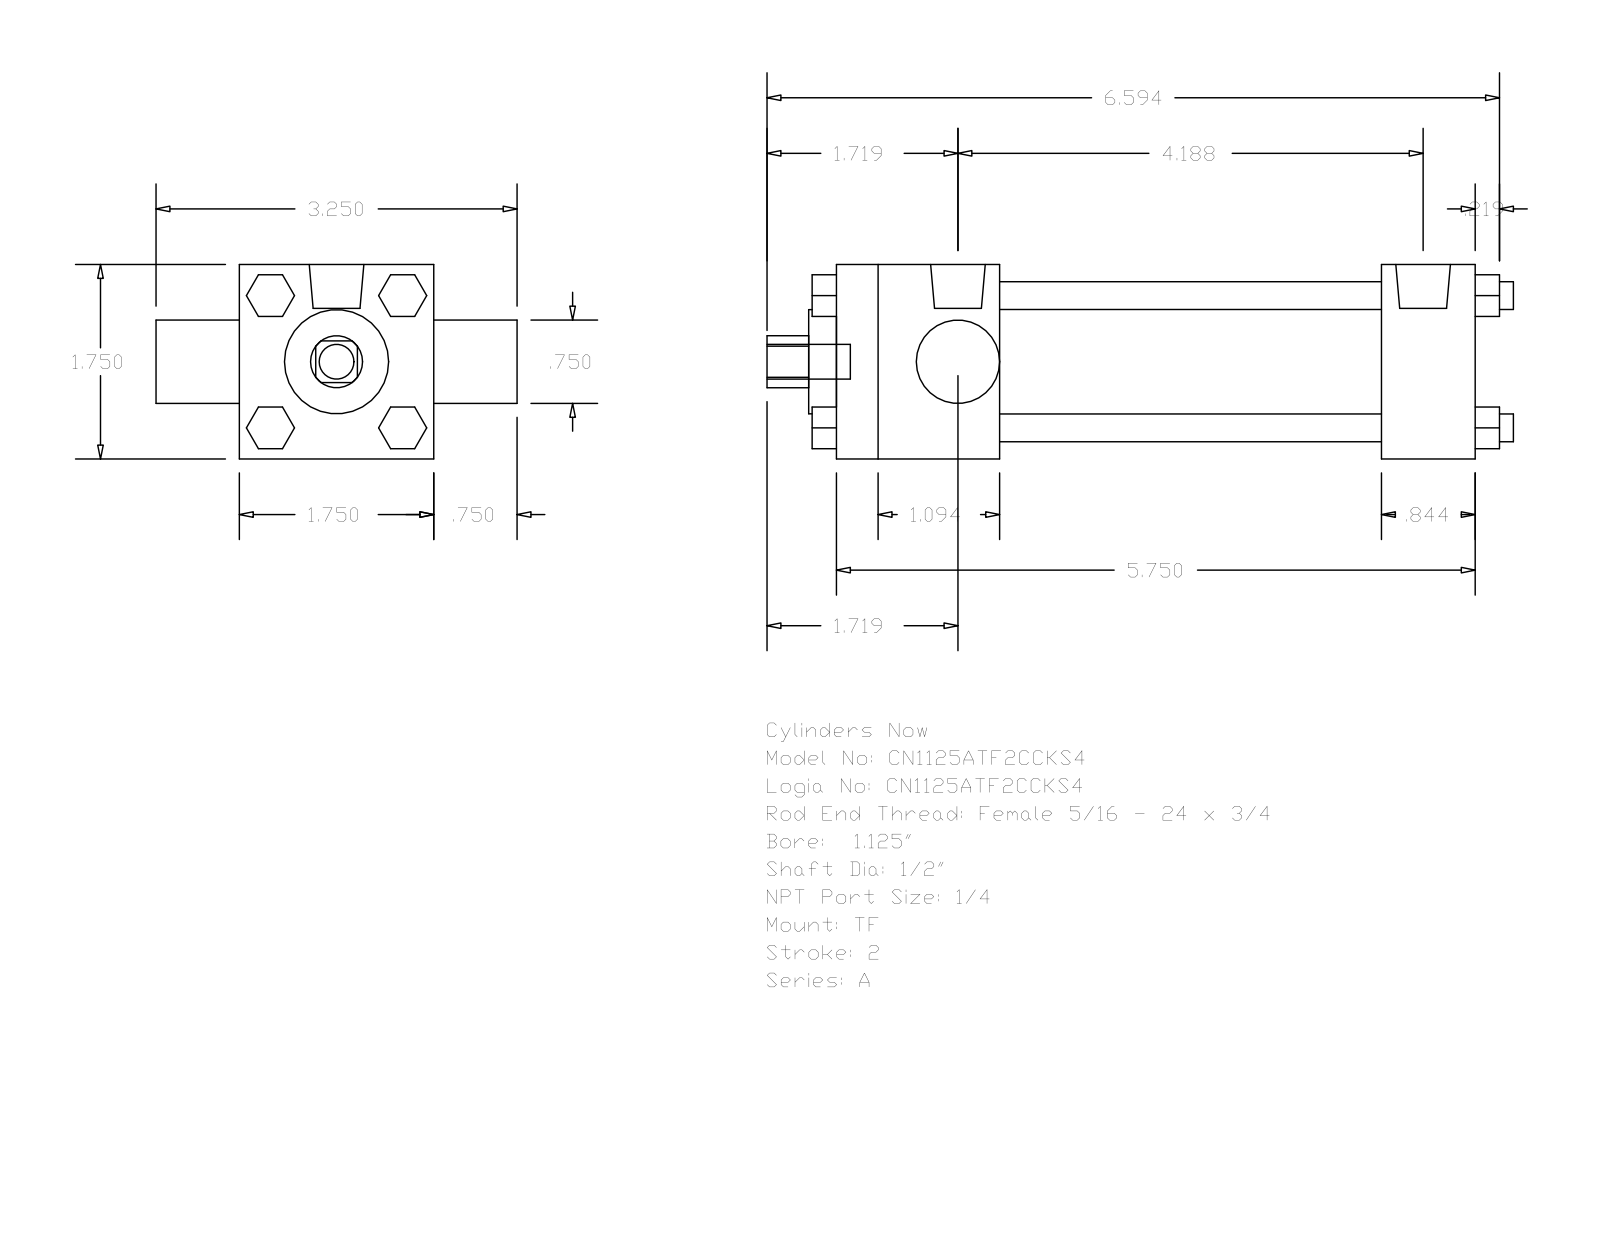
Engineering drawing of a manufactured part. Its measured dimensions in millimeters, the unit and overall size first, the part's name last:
Units: millimetres
Overall size (bounding box): 170.66 × 82.55 × 44.45
Round holes (diameter × count): ⌀12.7 ×1, ⌀19.05 ×1, ⌀23.81 ×1, ⌀31.88 ×1
Round bosses / shafts (diameter × count): ⌀6.35 ×4, ⌀5.56 ×3, ⌀12.49 ×2, ⌀7.94 ×1
Partial cylindrical surfaces — rounded edges, fillets, slot ends (radius × count): R5.94 ×1
Main face-to-face distances: 44.46, 146.05, 124.61, 21.44, 37.3, 87.31, 108.75, 19.04, 63.5, 9.53
Bodies: 0 solids, 120 faces (92 planar, 28 cylindrical, 0 other)
Part name (STEP PRODUCT): A_TF__0112_0.5
STEP written by: GSSL Pune (CONFIG_CONTROL_DESIGN)
